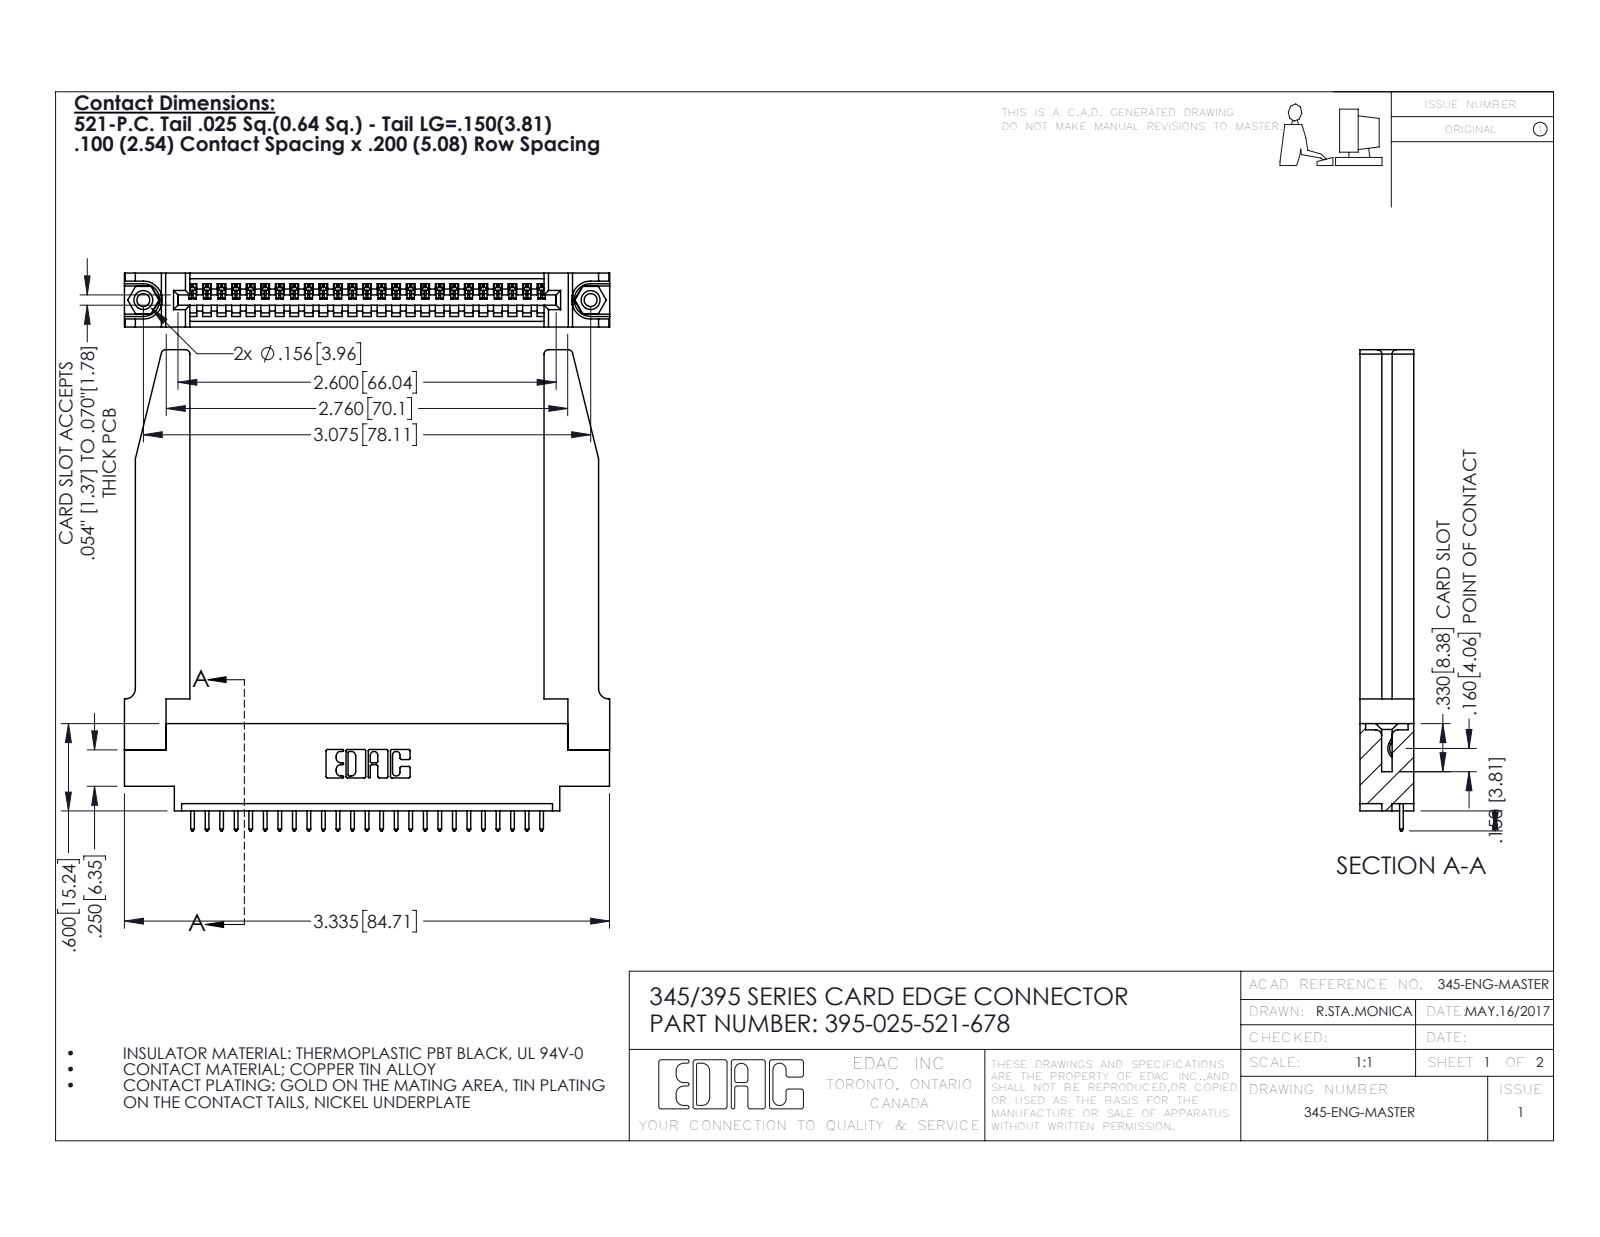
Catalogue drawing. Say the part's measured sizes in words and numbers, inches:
The part is named "345 Part_0.170 Offset - 0.156 Dia-TH; 395-025-521-678; 345-250-001_345-250-001-102; 345-292-001_345-293-121 (+1 more)". Its 3-D file was written by "SolidWorks 2016 (CONFIG_CONTROL_DESIGN)". It is 30 solids with 1814 faces: 1226 planar, 536 cylindrical and 52 other. Overall it measures 3.336 by 3.307 by 0.37 inches. Its volume is 0.946 cubic inches and its surface area 25.93 square inches. Round holes: 2 of diameter 0.089, 2 of diameter 0.125, 2 of diameter 0.156, 1 of diameter 0.064. Round bosses or shafts: 2 of diameter 0.155. Partial cylindrical surfaces (rounded edges, fillets, slot ends): 50 of radius 0.006, 50 of radius 0.01, 22 of radius 0.01, 8 of radius 0.03, 6 of radius 0.007, 6 of radius 0.031, 3 of radius 0.026, 2 of radius 0.031. The main face-to-face distances are 0.37, 0.072, 0.298, 0.098, 0.272, 0.025, 0.2, 0.148, 0.15, 0.225. The hole center spacings are 0.27, 2.84, 3.075.
